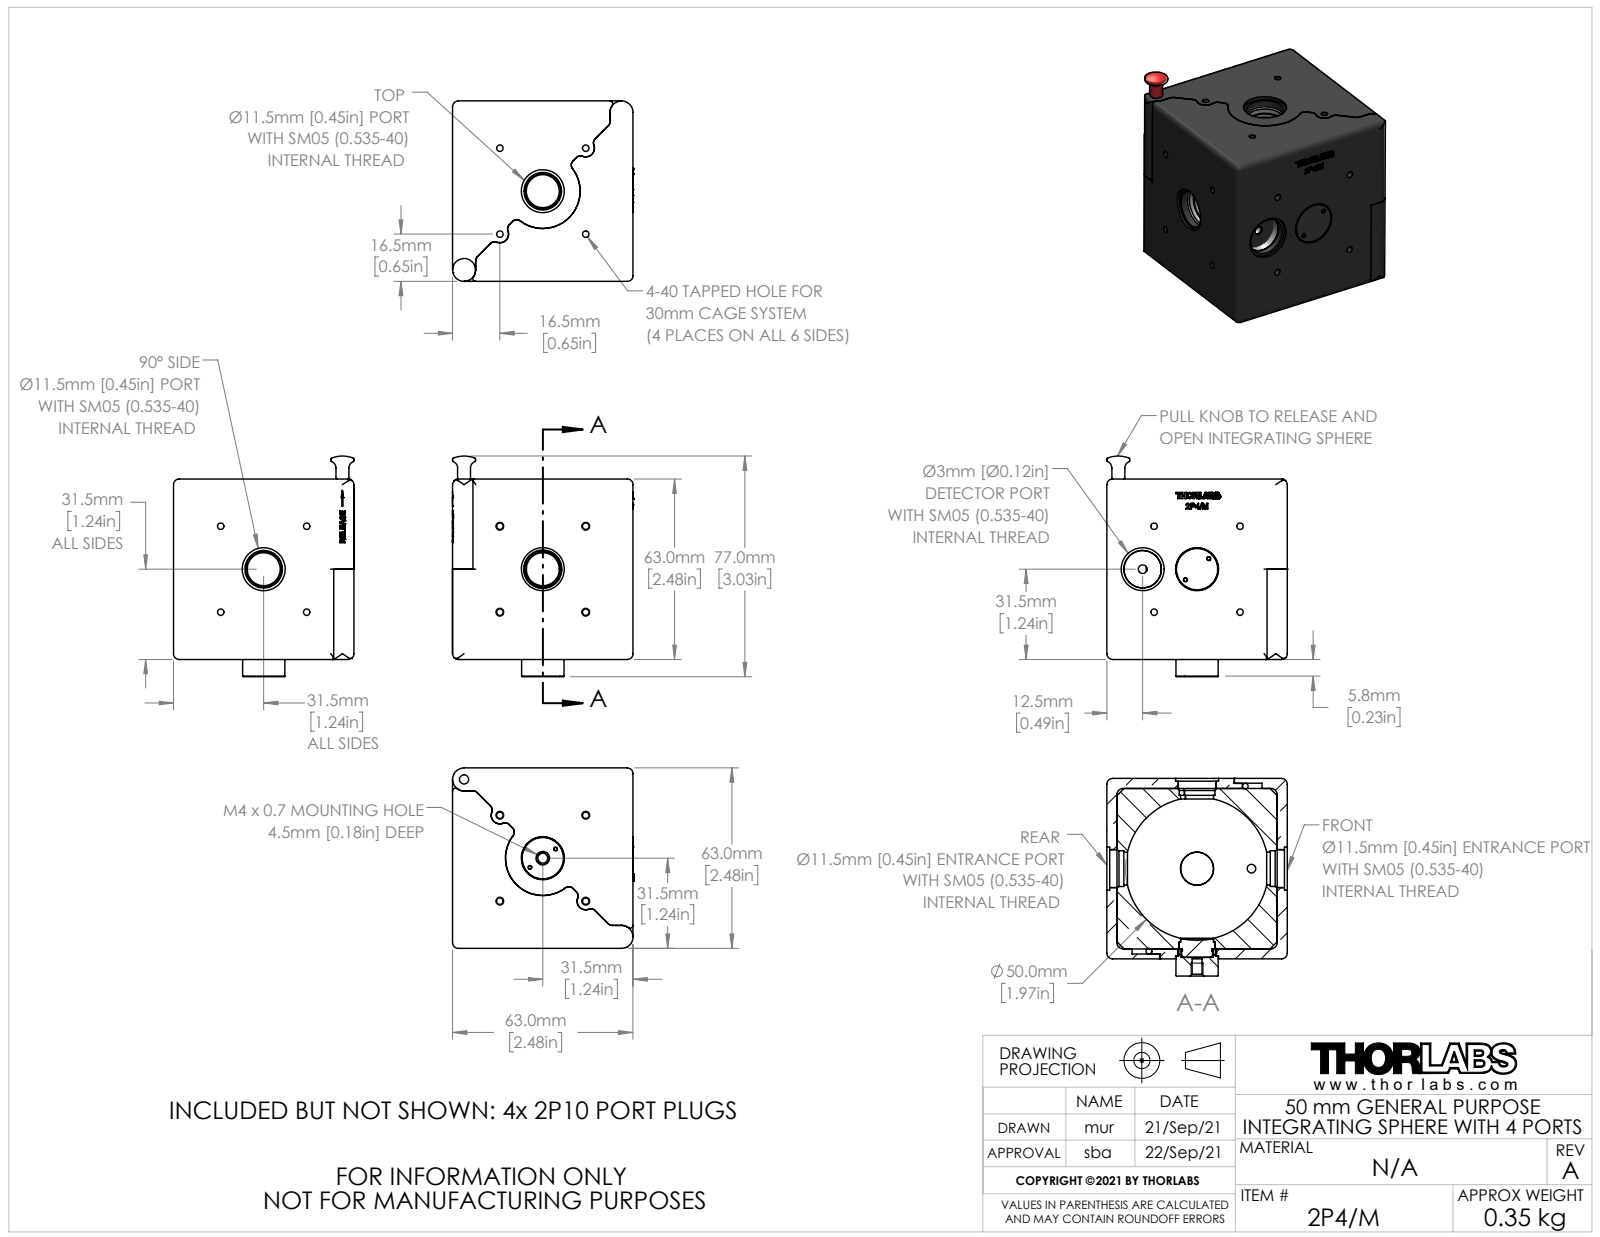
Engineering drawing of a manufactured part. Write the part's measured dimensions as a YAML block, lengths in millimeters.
part_name: "22.05.05_2P3_M WEB"
step_written_by: "SolidWorks 2019 (AUTOMOTIVE_DESIGN)"
units: millimeters
bodies: {solids: 29, faces: 5573, planar: 3554, cylindrical: 1402, other: 617}
overall_size: [77, 69.6, 69.6]
volume: 182529
surface_area: 87140
round_holes:
  - {diameter: 2.26, count: 12}
  - {diameter: 1.5, count: 6}
  - {diameter: 13.11, count: 5}
  - {diameter: 15, count: 5}
  - {diameter: 1.2, count: 4}
  - {diameter: 1.1, count: 3}
  - {diameter: 11.5, count: 3}
  - {diameter: 12.5, count: 3}
  - {diameter: 1.49, count: 2}
  - {diameter: 3, count: 2}
  - {diameter: 10.6, count: 2}
  - {diameter: 11.2, count: 2}
round_bosses_or_shafts:
  - {diameter: 14.8, count: 5}
  - {diameter: 13.56, count: 5}
  - {diameter: 12.6, count: 4}
  - {diameter: 2, count: 4}
  - {diameter: 13.18, count: 2}
  - {diameter: 12.55, count: 2}
  - {diameter: 10.78, count: 2}
  - {diameter: 26, count: 1}
partial_cylinders:
  - {radius: 2, count: 70}
  - {radius: 1.7, count: 32}
  - {radius: 1.79, count: 24}
  - {radius: 2.2, count: 24}
  - {radius: 1, count: 22}
  - {radius: 1.05, count: 16}
  - {radius: 1.35, count: 16}
  - {radius: 1.26, count: 12}
face_to_face_distances: [59.5, 3.5, 56, 63, 3.48, 59.52, 56.02, 56.04, 0.5, 3]
hole_center_spacings: [21.21, 30, 5.5, 42.43, 15.52, 37.16, 44.3, 12.87]
